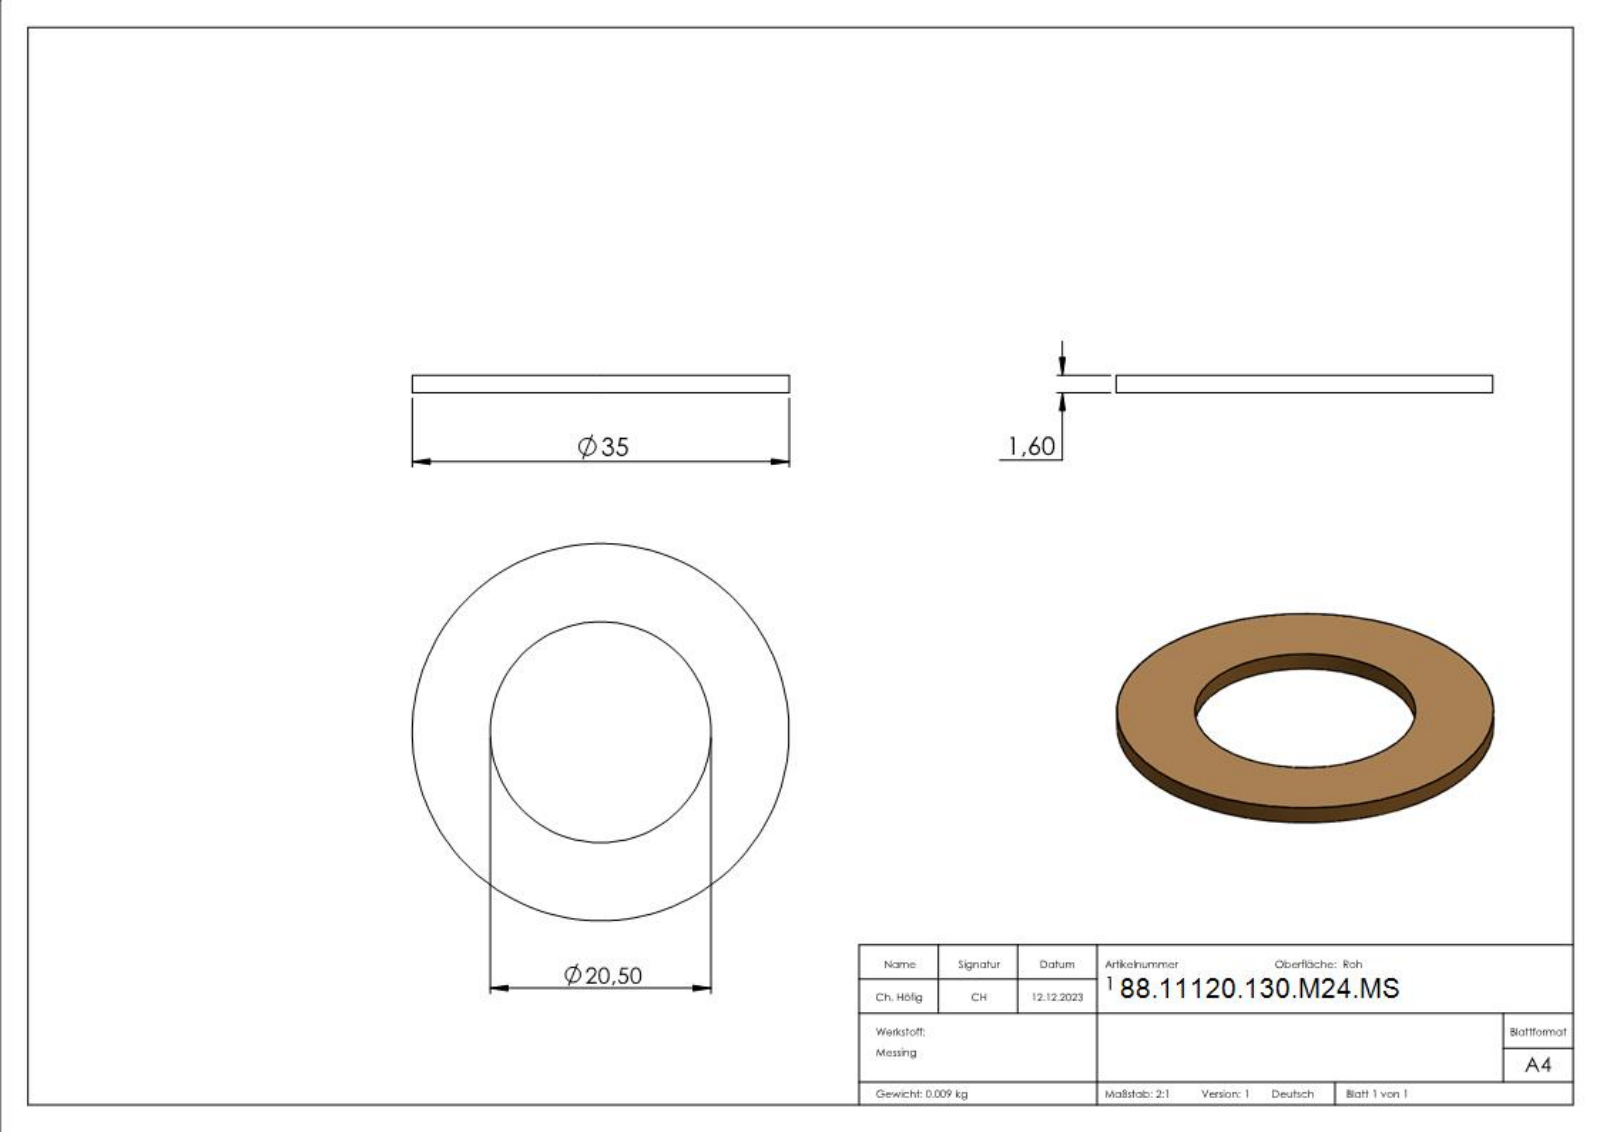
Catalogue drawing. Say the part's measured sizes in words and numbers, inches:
The part is named "120-130-M24-MS". Its 3-D file was written by "SolidWorks 2015 (CONFIG_CONTROL_DESIGN)". It is 1 solid with 275 faces: 164 planar, 4 cylindrical and 107 other. Overall it measures 1.378 by 1.378 by 0.059 inches. Its volume is 0.058 cubic inches and its surface area 2.368 square inches. Round holes: 1 of diameter 0.807. Round bosses or shafts: 1 of diameter 1.378. The main face-to-face distances are 0.059, 0.055, 0.034, 0.029, 0.03, 0.033, 1.058, 1.087, 1.075, 1.074.
